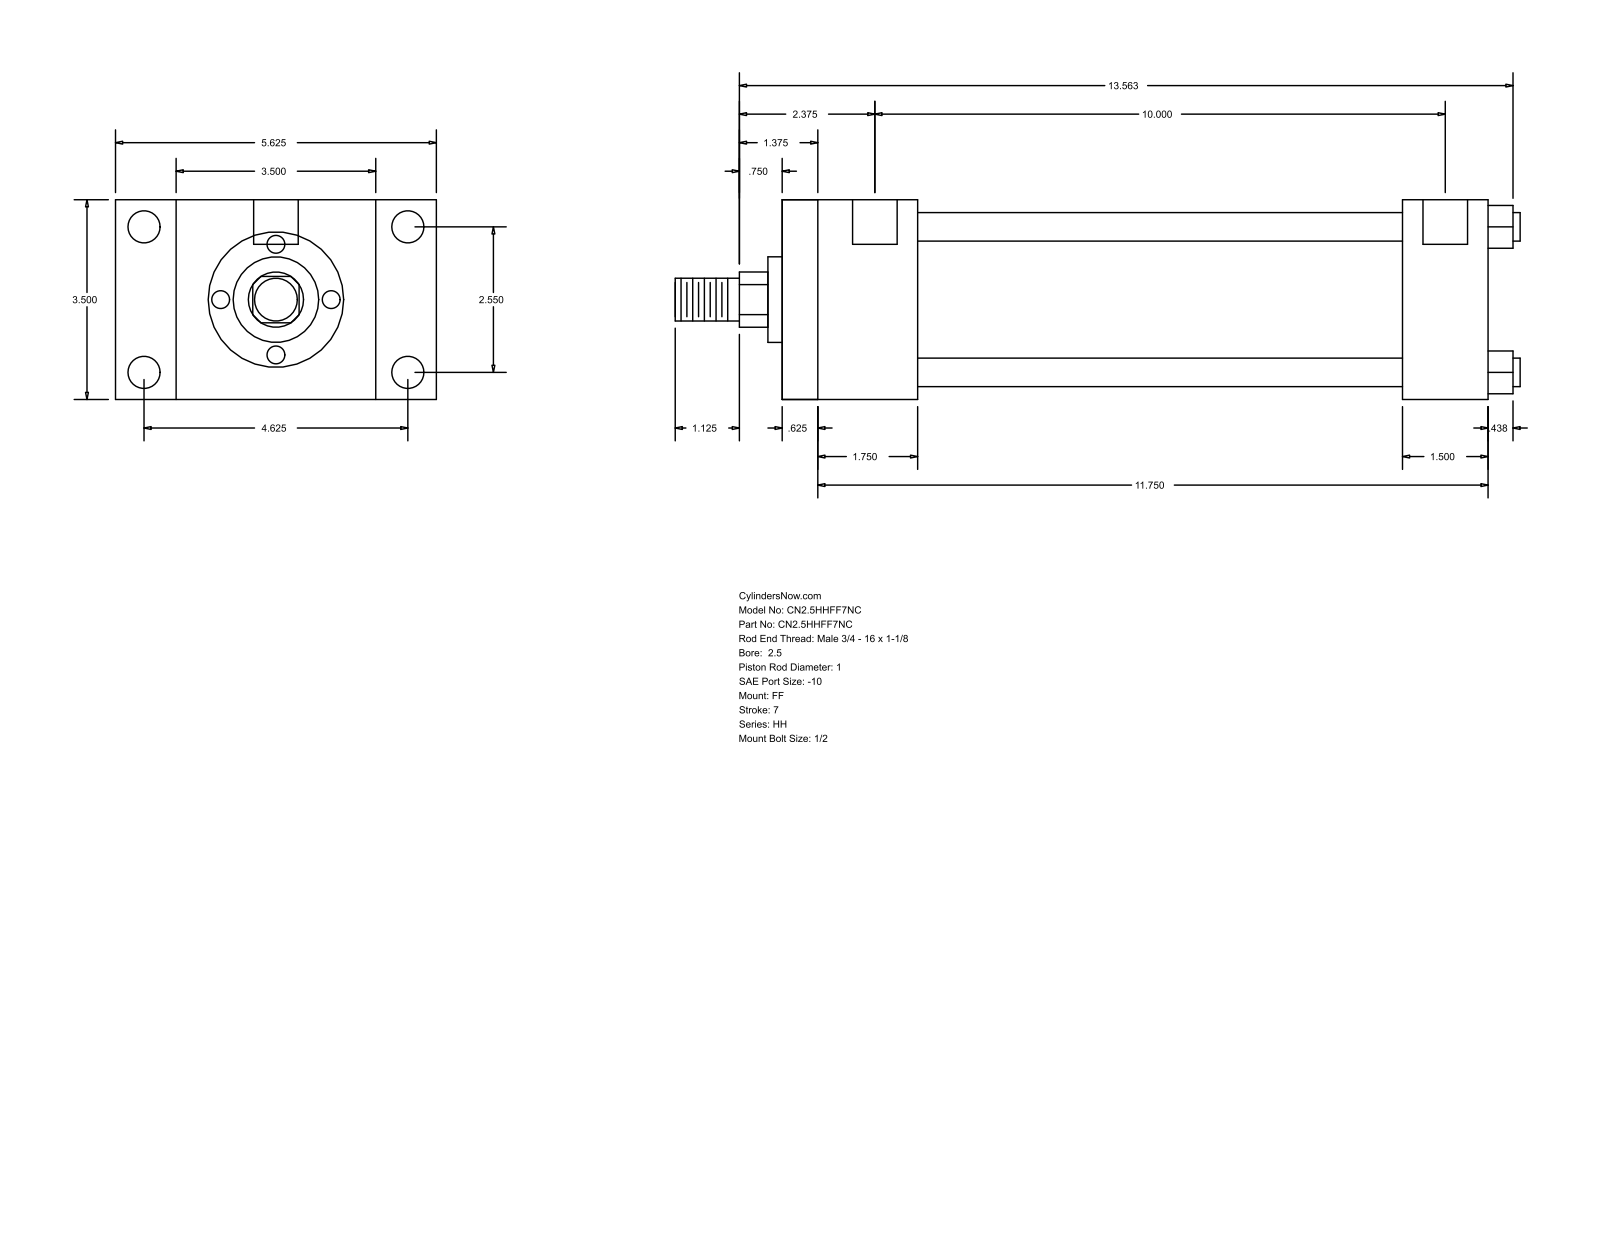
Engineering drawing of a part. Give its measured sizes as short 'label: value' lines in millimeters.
name: HH_FF__0250_1
written by: GSSL Pune (CONFIG_CONTROL_DESIGN)
unit: mm
bodies: 0 solids, 92 faces (64 planar, 28 cylindrical, 0 other)
size: 376.24 × 142.88 × 88.9
holes: 4× ⌀5.56, 4× ⌀14.3, 2× ⌀19.84
bosses: 4× ⌀12.7, 1× ⌀73.03, 1× ⌀38.1, 1× ⌀25.4, 1× ⌀19.05
rounds: 1× R12.29
face distances: 88.9, 314.33, 15.87, 298.46, 60.33, 44.46, 254, 276.22, 260.35, 215.89
hole spacings: 1.59, 64.76, 117.48, 134.15, 255.58, 257.17, 253.99
